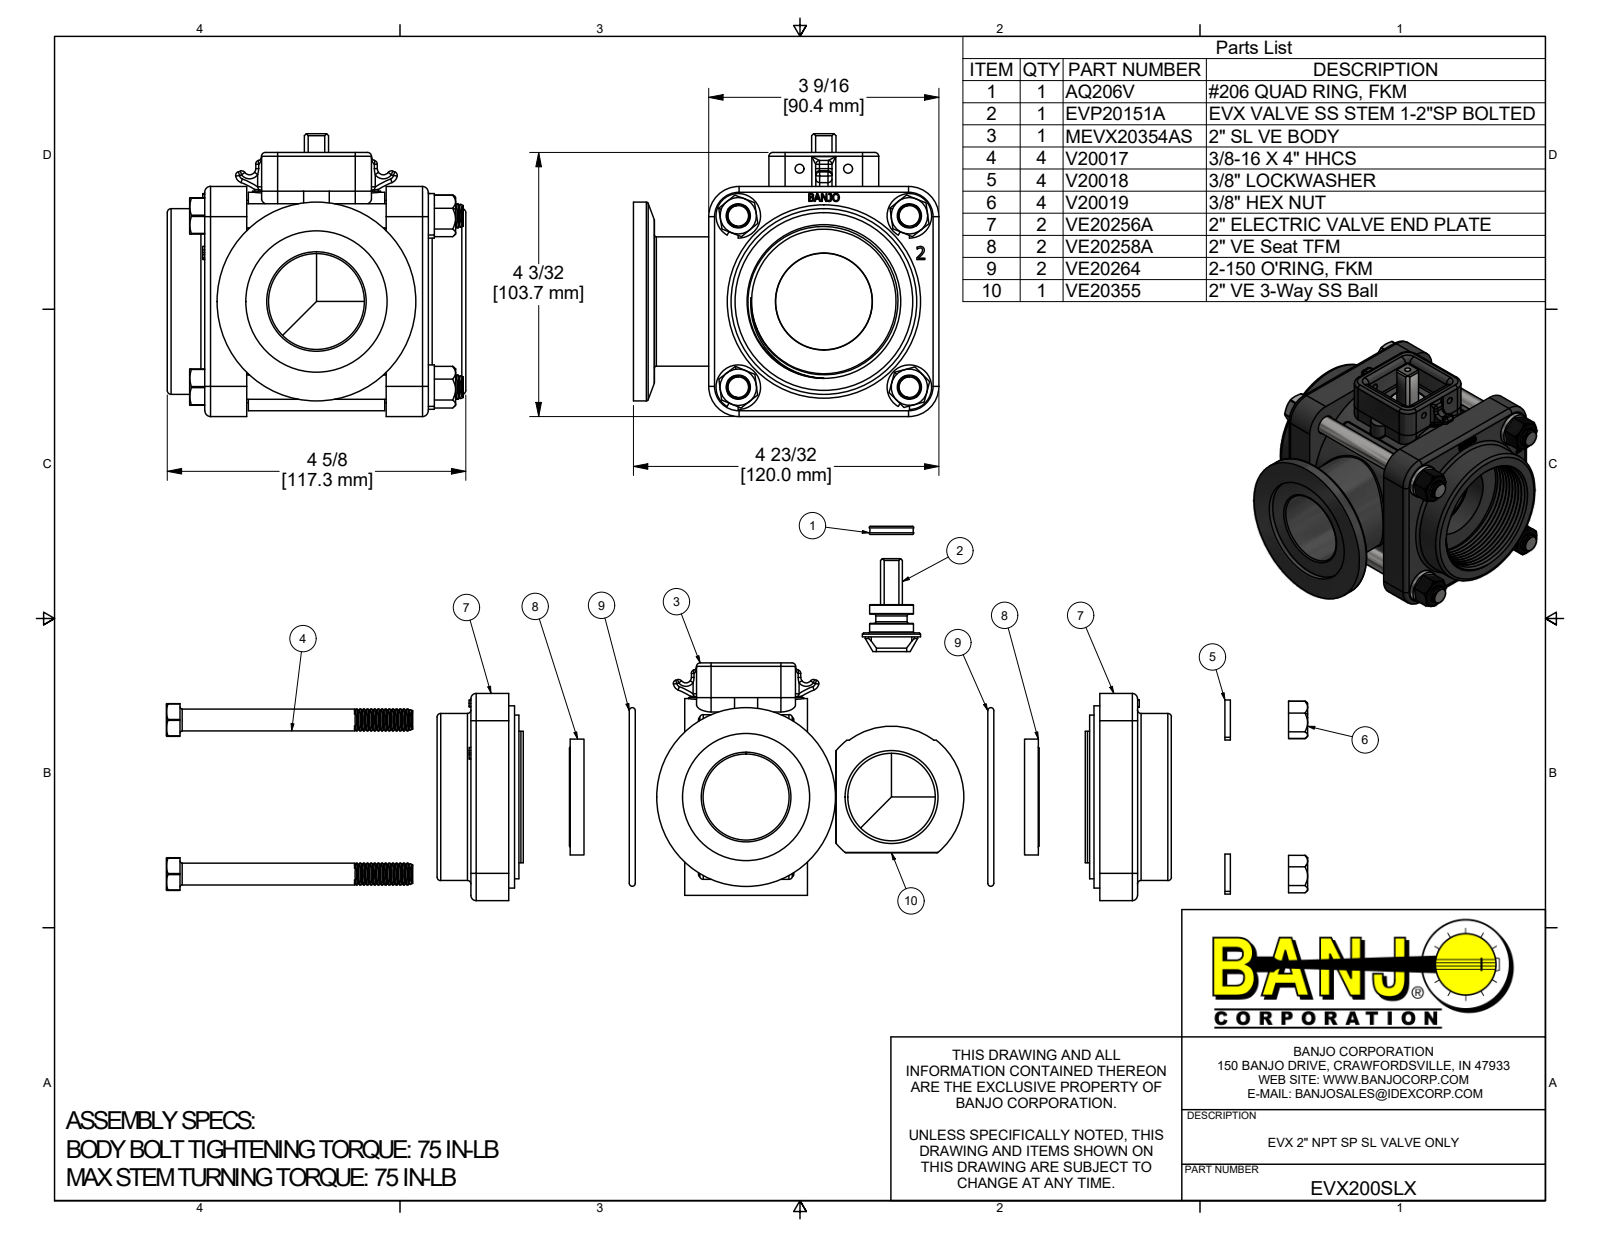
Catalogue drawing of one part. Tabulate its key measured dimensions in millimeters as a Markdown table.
| quantity | value |
| --- | --- |
| part name | EVX200SLX; MEVX20354AS; MEVX20354ASX; V20017 (+8 more) |
| STEP written by | Autodesk Inventor 2019 (AUTOMOTIVE_DESIGN) |
| units | millimeters |
| bodies | 22 solids, 1283 faces (340 planar, 403 cylindrical, 540 other) |
| overall size | 120 × 117.3 × 111.1 |
| volume | 536 700 mm³ |
| surface area | 174 500 mm² |
| round holes (diameter × count) | 7.8 × 4, 9.8 × 4, 10.3 × 4, 38.1 × 3, 3.4 × 2, 19.3 × 1, 25.9 × 1, 37.6 × 1, 38 × 1, 50.7 × 1, 55.5 × 1, 56.8 × 1 |
| round bosses / shafts (diameter × count) | 8.2 × 60, 17.4 × 4, 9.5 × 4, 85.9 × 1, 79.5 × 1, 78.1 × 1, 72.9 × 1, 71.4 × 1 |
| partial cylindrical surfaces (radius × count) | 1.5 × 28, 2.3 × 12, 0.5 × 8, 4.1 × 8, 3.2 × 6, 0.4 × 4, 0.8 × 4, 5.3 × 4 |
| main face-to-face distances | 71.3, 16.5, 21, 66.9, 4.4, 50.4, 90.4, 2.5, 9.4, 7.1 |
| hole center spacings | 47.5, 67.3, 30.4, 47, 53, 89.1, 95.1, 96 |
